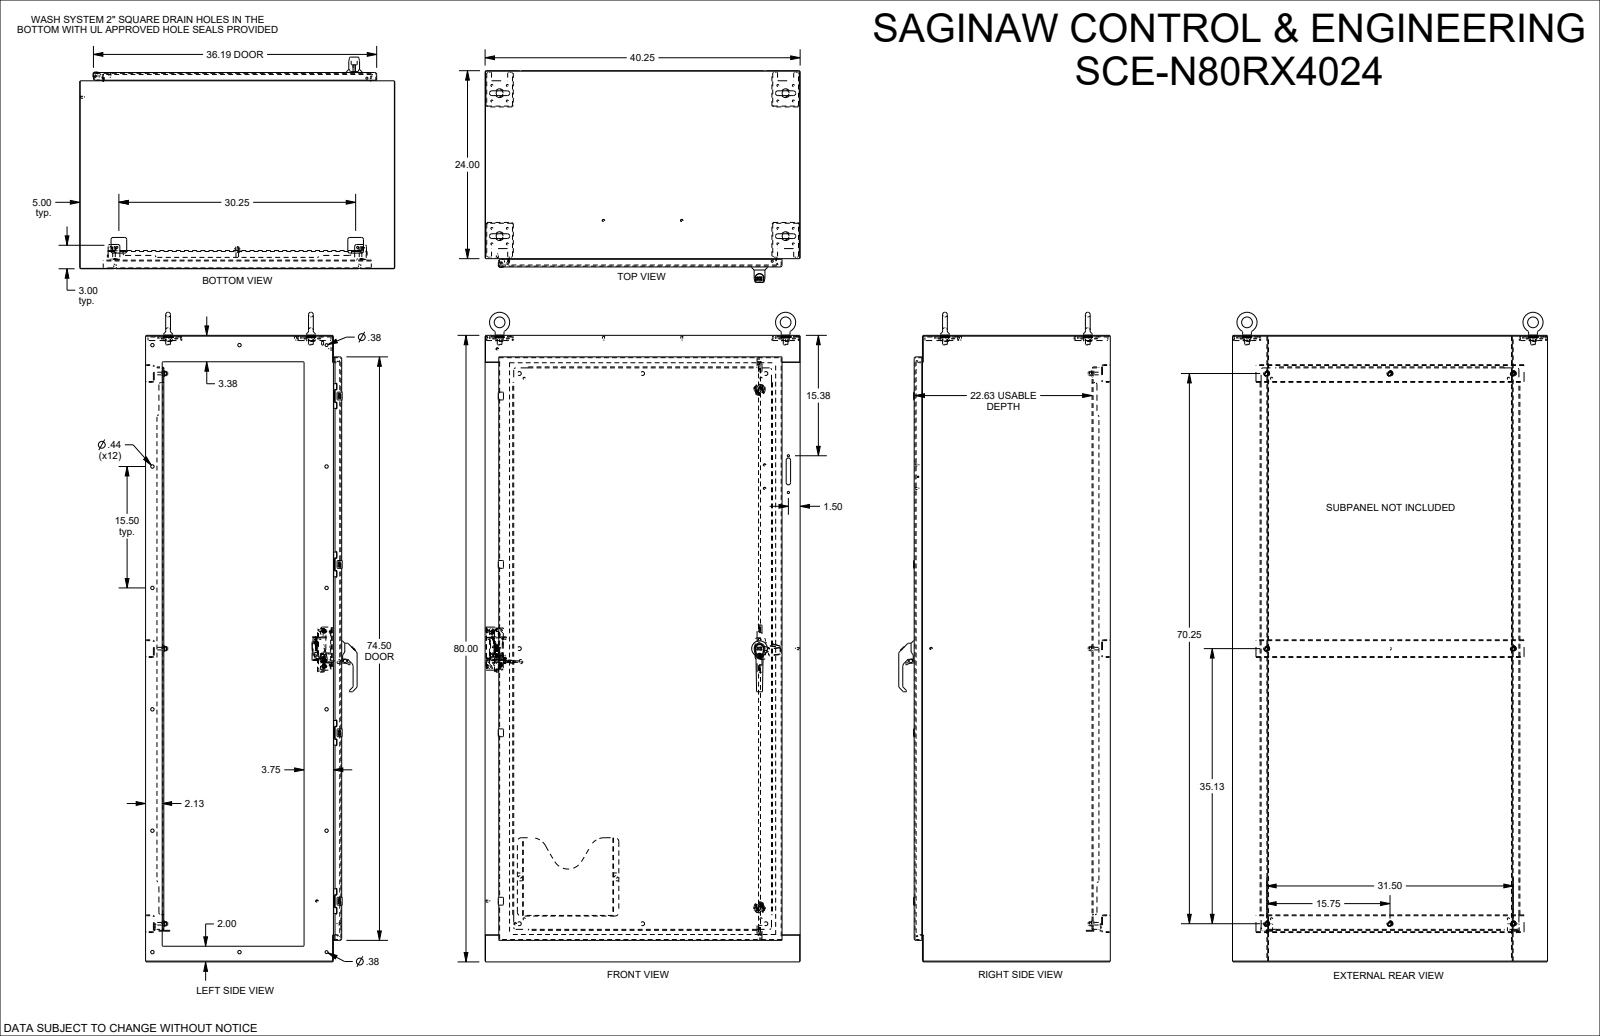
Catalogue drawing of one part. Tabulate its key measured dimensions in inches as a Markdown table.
| quantity | value |
| --- | --- |
| part name | SCE-N80RX4024 |
| STEP written by | SolidWorks 2023 (AUTOMOTIVE_DESIGN) |
| units | inches |
| bodies | 27 solids, 4266 faces (1638 planar, 1520 cylindrical, 1108 other) |
| overall size | 80 × 40.25 × 27.046 |
| volume | 1 291 in³ |
| surface area | 24 604 in² |
| round holes (diameter × count) | 0.25 × 18, 0.437 × 12, 0.375 × 10, 0.205 × 8, 0.244 × 8, 0.04 × 4, 0.17 × 4, 0.218 × 4, 0.256 × 4, 0.875 × 4, 0.115 × 3, 0.2 × 3 |
| round bosses / shafts (diameter × count) | 0.17 × 12, 0.25 × 10, 0.24 × 8, 0.196 × 5, 1.4 × 2, 0.48 × 2, 0.341 × 2, 0.3 × 2 |
| partial cylindrical surfaces (radius × count) | 0.03 × 142, 0.015 × 108, 0.125 × 83, 0.063 × 43, 0.167 × 38, 0.04 × 37, 0.229 × 32, 0.25 × 26 |
| main face-to-face distances | 0.104, 24.954, 24.85, 25.058, 0.104, 79.896, 23.896, 1.058, 40.146, 79.792 |
| hole center spacings | 1.979, 1.4, 21.5, 15.5, 27.117, 2.799, 17.289, 18.25 |
